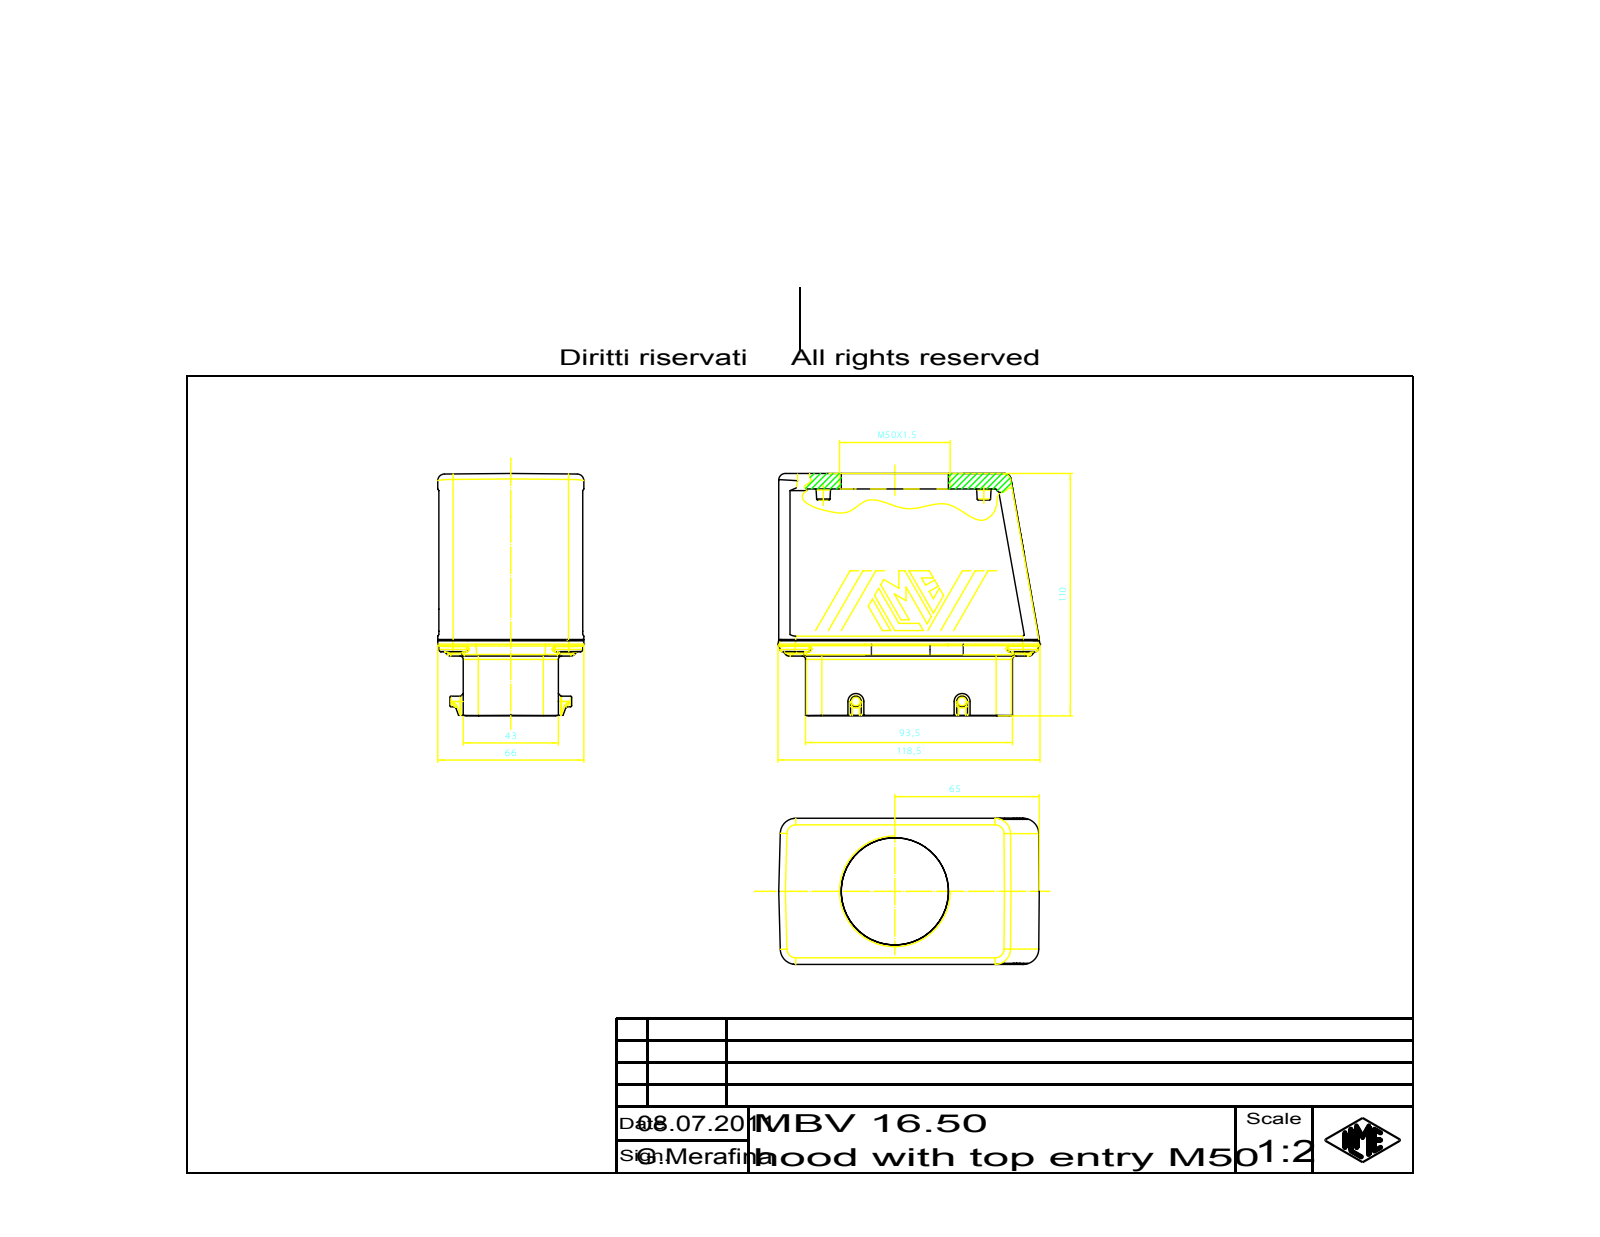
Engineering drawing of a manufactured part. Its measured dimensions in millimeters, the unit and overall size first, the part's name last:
Units: millimetres
Overall size (bounding box): 117.26 × 108.97 × 66.01
Round holes (diameter × count): ⌀50 ×1
Round bosses / shafts (diameter × count): ⌀4.8 ×2
Partial cylindrical surfaces — rounded edges, fillets, slot ends (radius × count): R1 ×44, R0.3 ×18, R7 ×12, R3 ×10, R0.5 ×8, R1.5 ×6, R4.2 ×4, R5 ×4
Main face-to-face distances: 65.01, 82.21, 0.4, 65.41, 25, 57.21, 11, 54.01, 54, 43
Volume: 562 328 mm³ · Surface area: 60 839 mm²
Bodies: 1 solid, 647 faces (333 planar, 150 cylindrical, 164 other)
Part name (STEP PRODUCT): 53848_Body_1
STEP written by: CoCreate Modeling 16.00A 16-Aug-2008 (C) Parametric Technology GmbH (AUTOMOTIVE_DESIGN)
